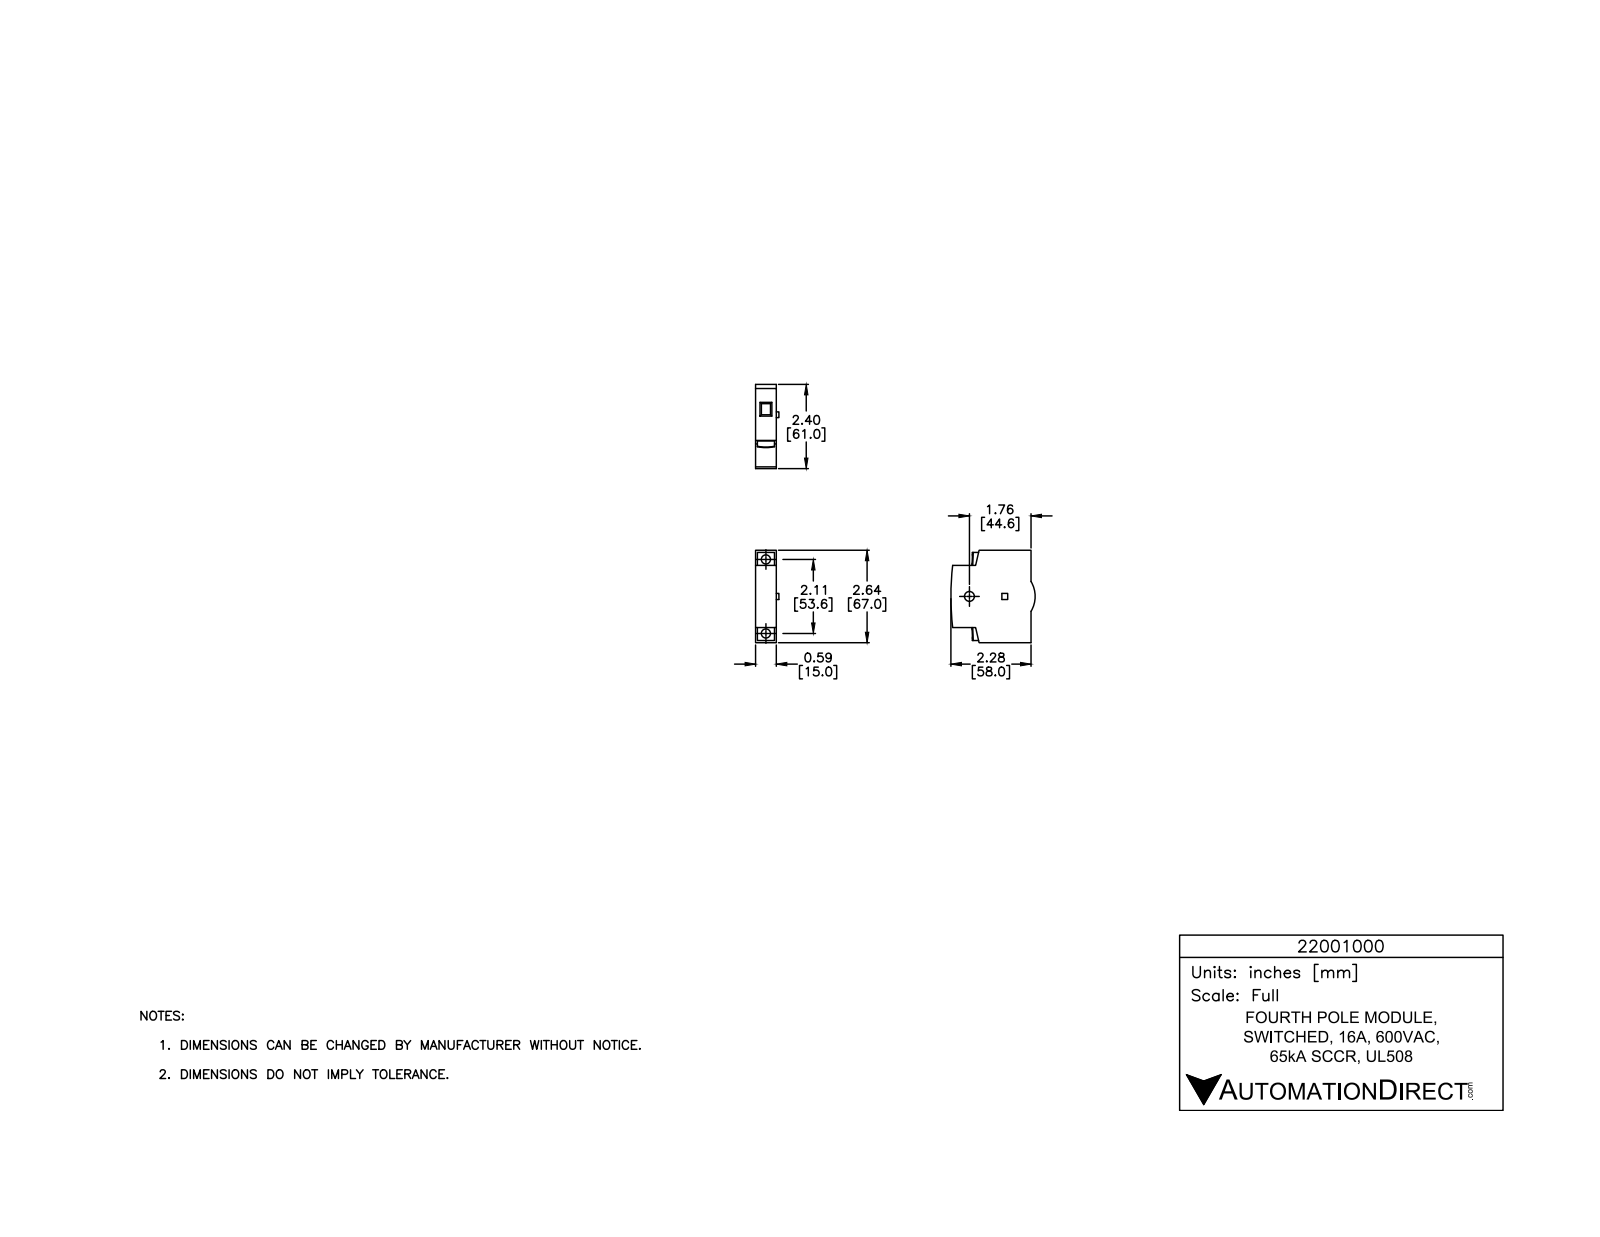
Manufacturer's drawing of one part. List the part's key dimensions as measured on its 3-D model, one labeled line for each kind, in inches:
Part name (STEP PRODUCT): 22001000-UL
STEP written by: SolidWorks 2021 (CONFIG_CONTROL_DESIGN)
Units: inches
Bodies: 1 solid, 61 faces (46 planar, 11 cylindrical, 4 other)
Overall size (bounding box): 2.638 × 2.402 × 0.665
Volume: 3.141 in³ · Surface area: 18.13 in²
Round holes (diameter × count): ⌀0.26 ×2, ⌀0.283 ×1
Partial cylindrical surfaces — rounded edges, fillets, slot ends (radius × count): R0.827 ×1, R7.874 ×1
Main face-to-face distances: 0.591, 2.638, 0.433, 2.205, 1.772, 0.063, 2.575, 0.37, 2.142, 0.051
Hole centre spacings: 2.11
